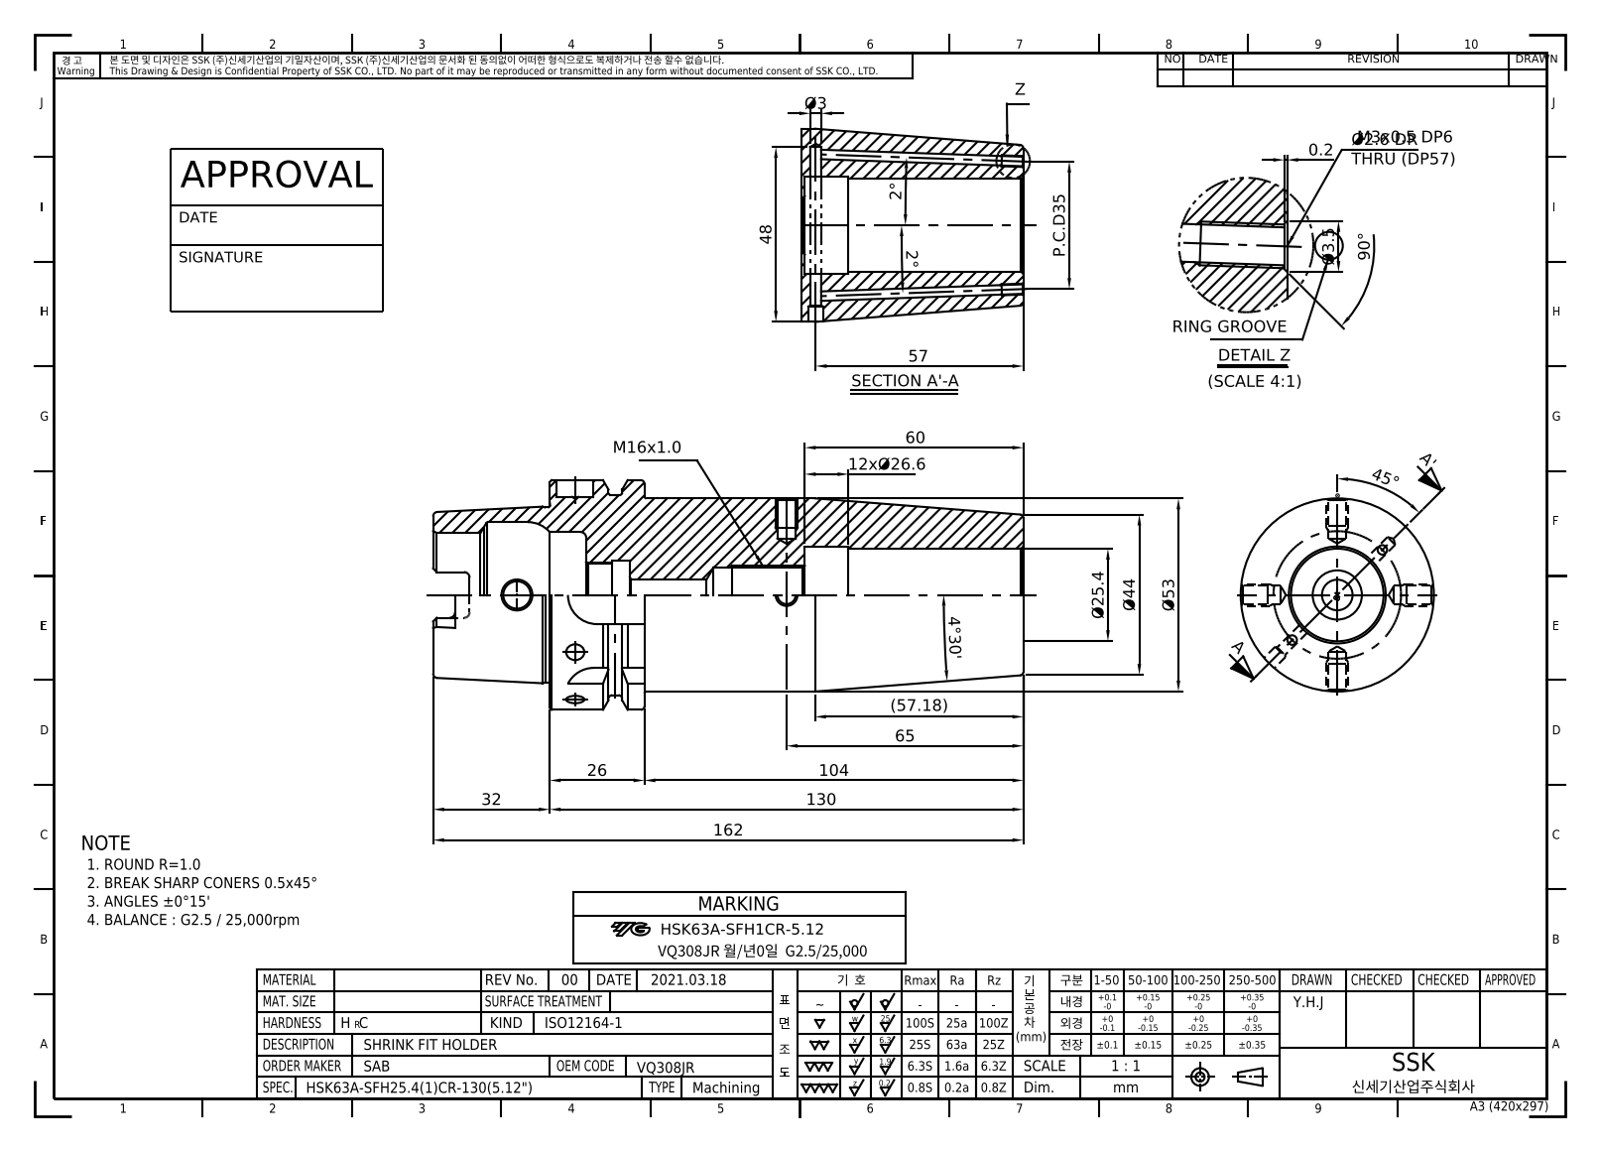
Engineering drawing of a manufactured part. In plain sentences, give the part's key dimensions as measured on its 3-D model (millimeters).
The part is named "LO-HSK63A-SFH25.4CR-130". Its 3-D file was written by "Autodesk Inventor 2022 (AUTOMOTIVE_DESIGN)". It is 1 solid with 124 faces: 44 planar, 36 cylindrical and 44 other. Overall it measures 162 by 63 by 63 millimeters. Its volume is 253 864 cubic millimeters and its surface area 45 320 square millimeters. Round holes: 2 of diameter 2.46, 1 of diameter 7.5, 1 of diameter 8.4, 1 of diameter 10, 1 of diameter 14.92, 1 of diameter 16.92, 1 of diameter 19, 1 of diameter 25.4, 1 of diameter 26.6, 1 of diameter 34, 1 of diameter 40. Round bosses or shafts: 1 of diameter 63, 1 of diameter 55, 1 of diameter 53, 1 of diameter 48.04. Partial cylindrical surfaces (rounded edges, fillets, slot ends): 6 of radius 1.5, 4 of radius 2.88, 4 of radius 8. The main face-to-face distances are 60, 130, 10, 120, 32, 48, 53, 70, 42, 102.
